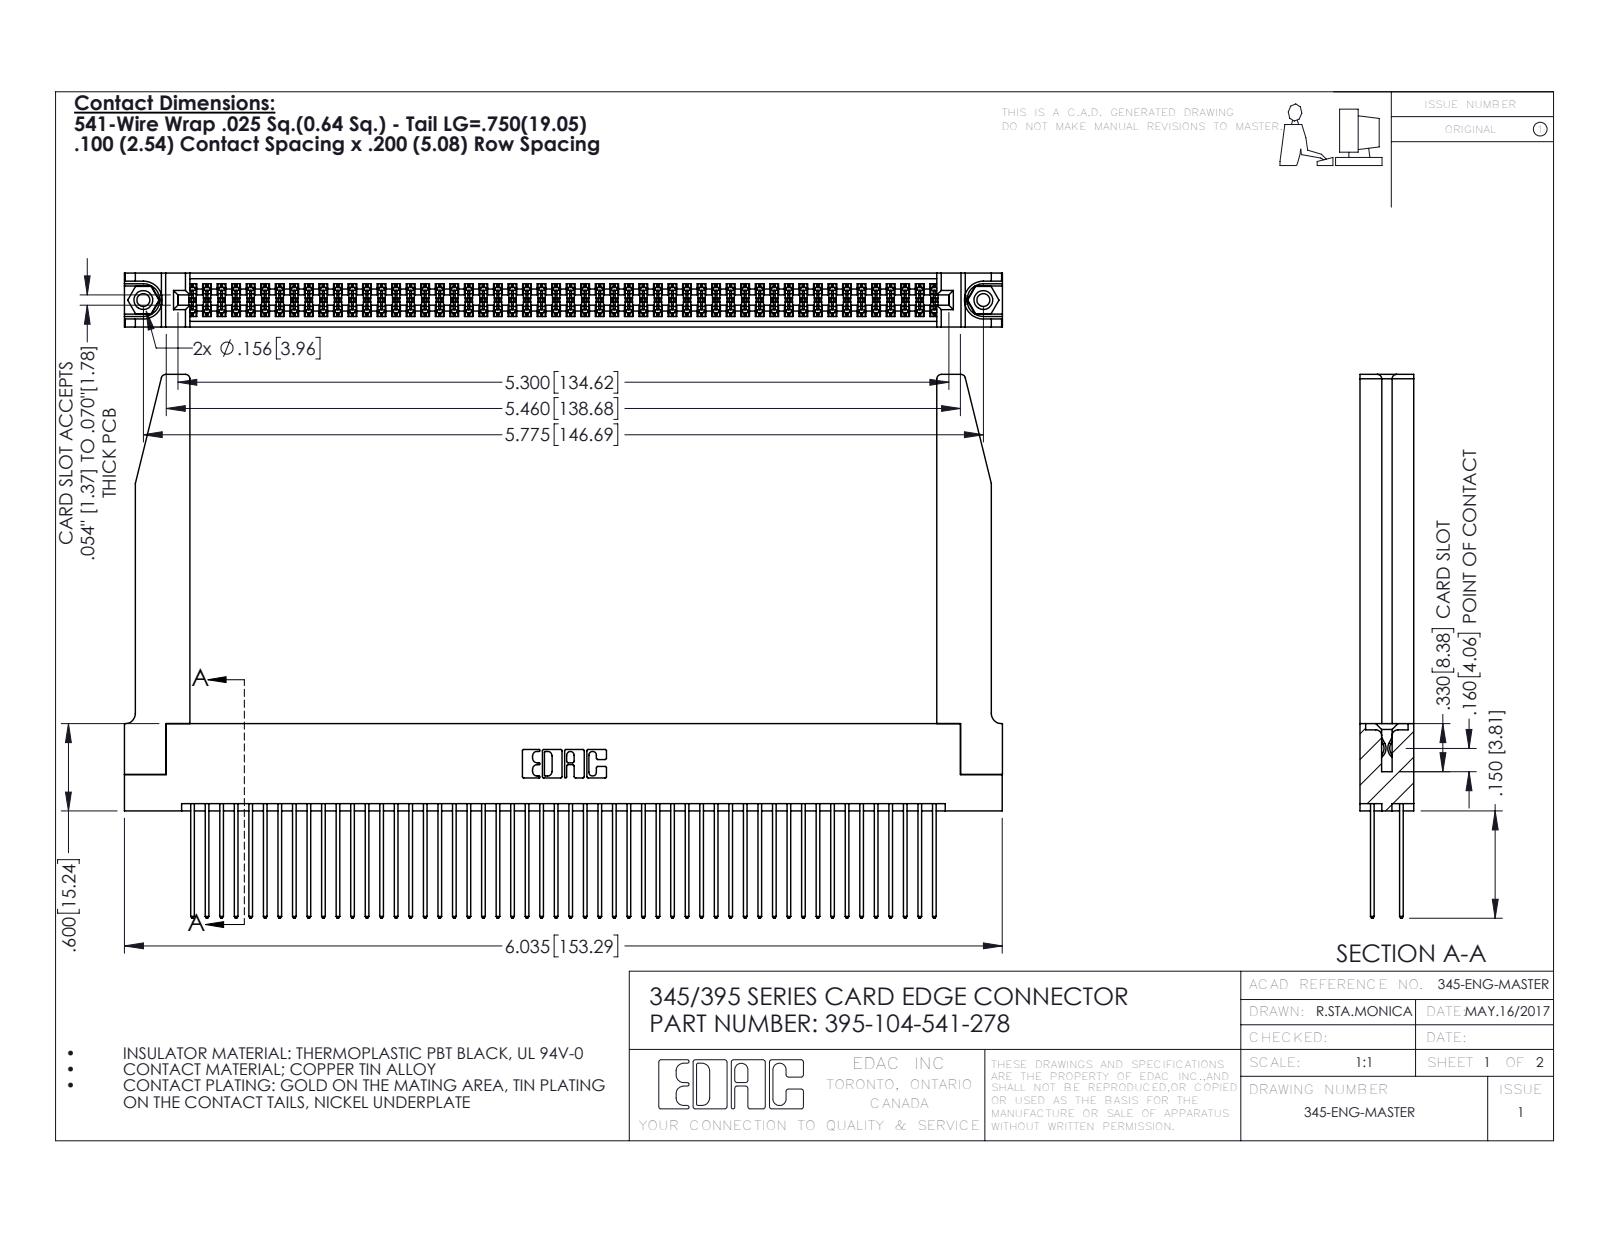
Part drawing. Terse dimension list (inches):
name: 345-292-001_345-293-141; 395-104-541-278; 345-250-001_345-250-001-102; 345 Part_Flush Mounting Lugs - 0.156 Dia-TH (+1 more)
written by: SolidWorks 2016 (CONFIG_CONTROL_DESIGN)
unit: in
bodies: 109 solids, 5560 faces (3654 planar, 1854 cylindrical, 52 other)
size: 6.036 × 3.737 × 0.37
volume: 1.425 in³; area: 50.95 in²
holes: 2× ⌀0.089, 2× ⌀0.125, 2× ⌀0.156, 1× ⌀0.064
bosses: 2× ⌀0.155
rounds: 156× R0.006, 104× R0.01, 22× R0.01, 8× R0.03, 6× R0.007, 6× R0.031, 3× R0.026, 2× R0.014
face distances: 0.072, 0.298, 0.2, 0.37, 0.098, 0.272, 0.025, 0.225, 0.175, 0.15
hole spacings: 0.27, 5.539, 5.775
